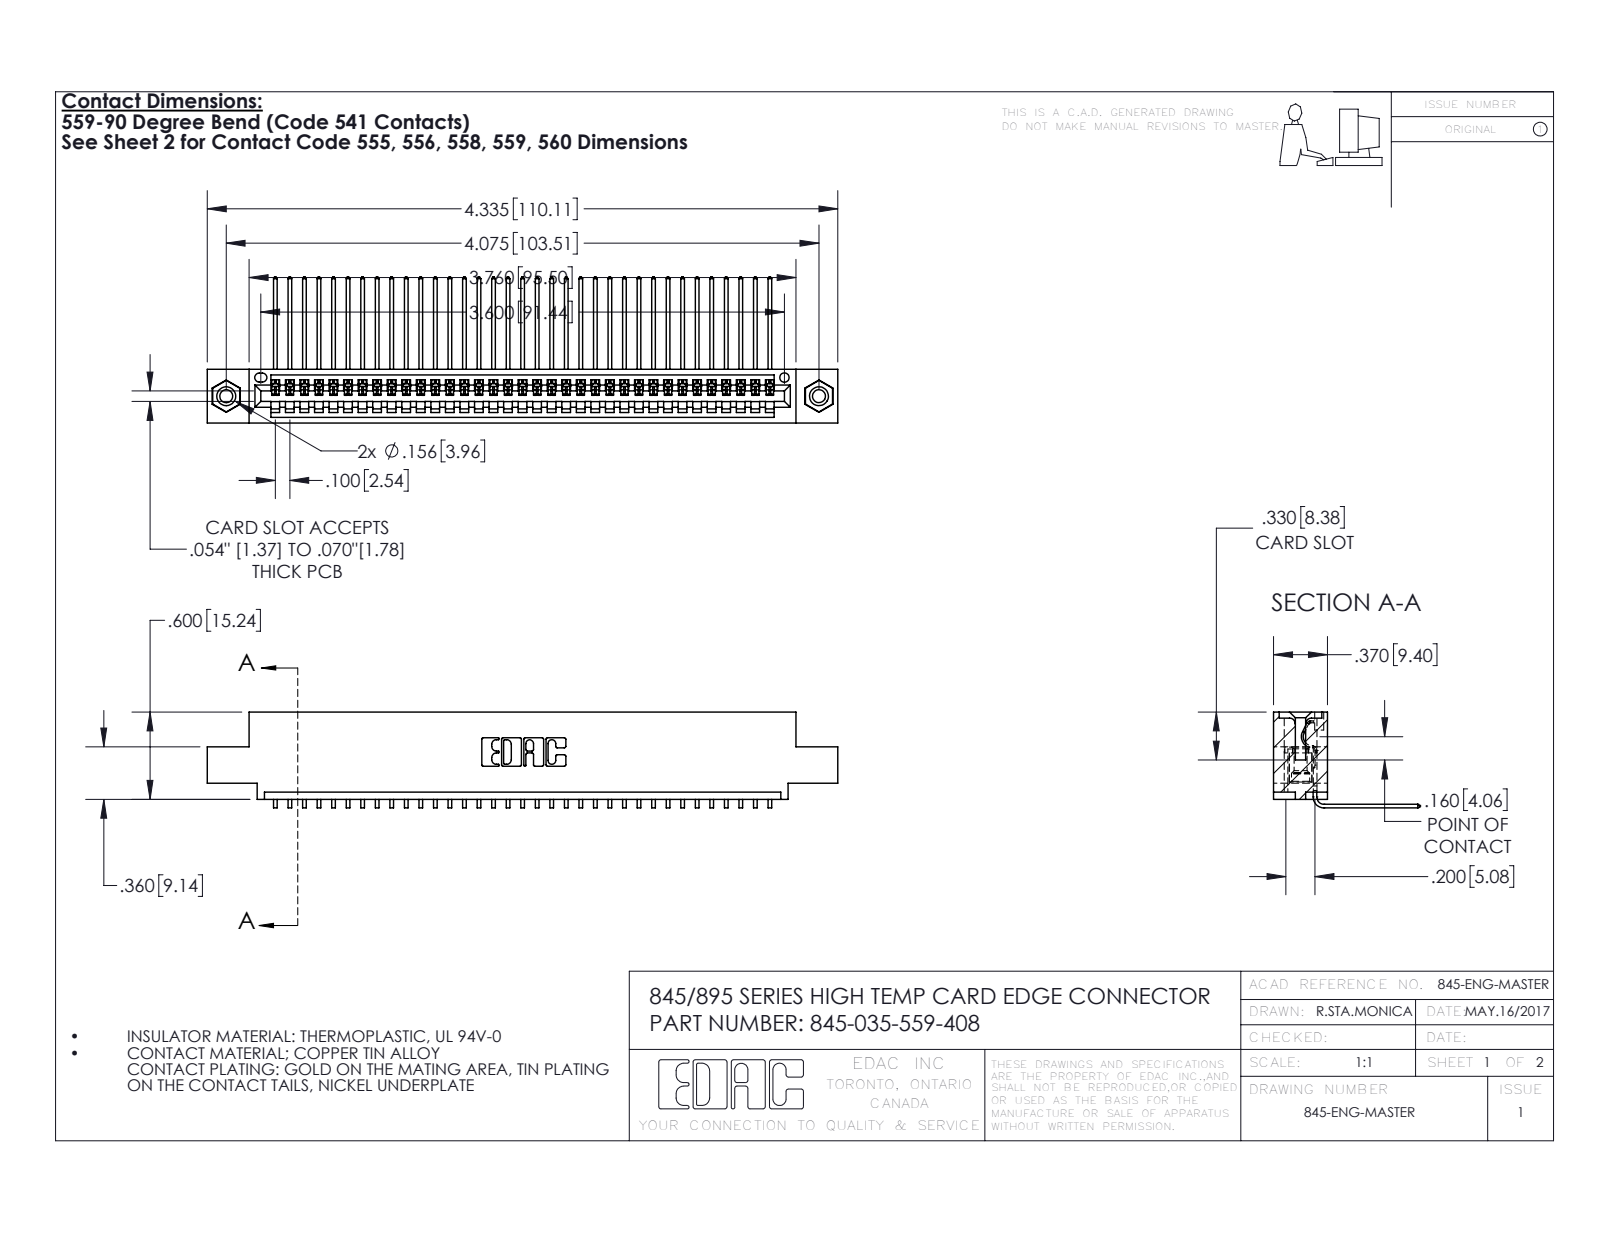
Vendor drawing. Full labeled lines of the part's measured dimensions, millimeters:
Part name (STEP PRODUCT): 345 Part_0.110 Offset - 0.156 Dia-TI; 345-292-001_558 559 Tail - 1; 345-250-001_345-250-003-102; 345-035-559-408
STEP written by: SolidWorks 2016 (CONFIG_CONTROL_DESIGN)
Units: millimetres
Bodies: 38 solids, 2290 faces (1586 planar, 688 cylindrical, 16 other)
Overall size (bounding box): 110.1 × 25.5 × 16.7
Volume: 10 400 mm³ · Surface area: 14 560 mm²
Round holes (diameter × count): ⌀2.3 ×2, ⌀3.2 ×2, ⌀4 ×2, ⌀1.6 ×1
Round bosses / shafts (diameter × count): ⌀3.9 ×2
Partial cylindrical surfaces — rounded edges, fillets, slot ends (radius × count): R0.2 ×70, R0.3 ×22, R0.2 ×6, R0.8 ×6, R0.7 ×3, R0.8 ×2, R1 ×2, R0.4 ×1
Main face-to-face distances: 1.8, 7.6, 9.4, 5.1, 2.5, 6.9, 0.6, 5.7, 3.8, 1.8
Hole centre spacings: 6.9, 97.5, 103.5
